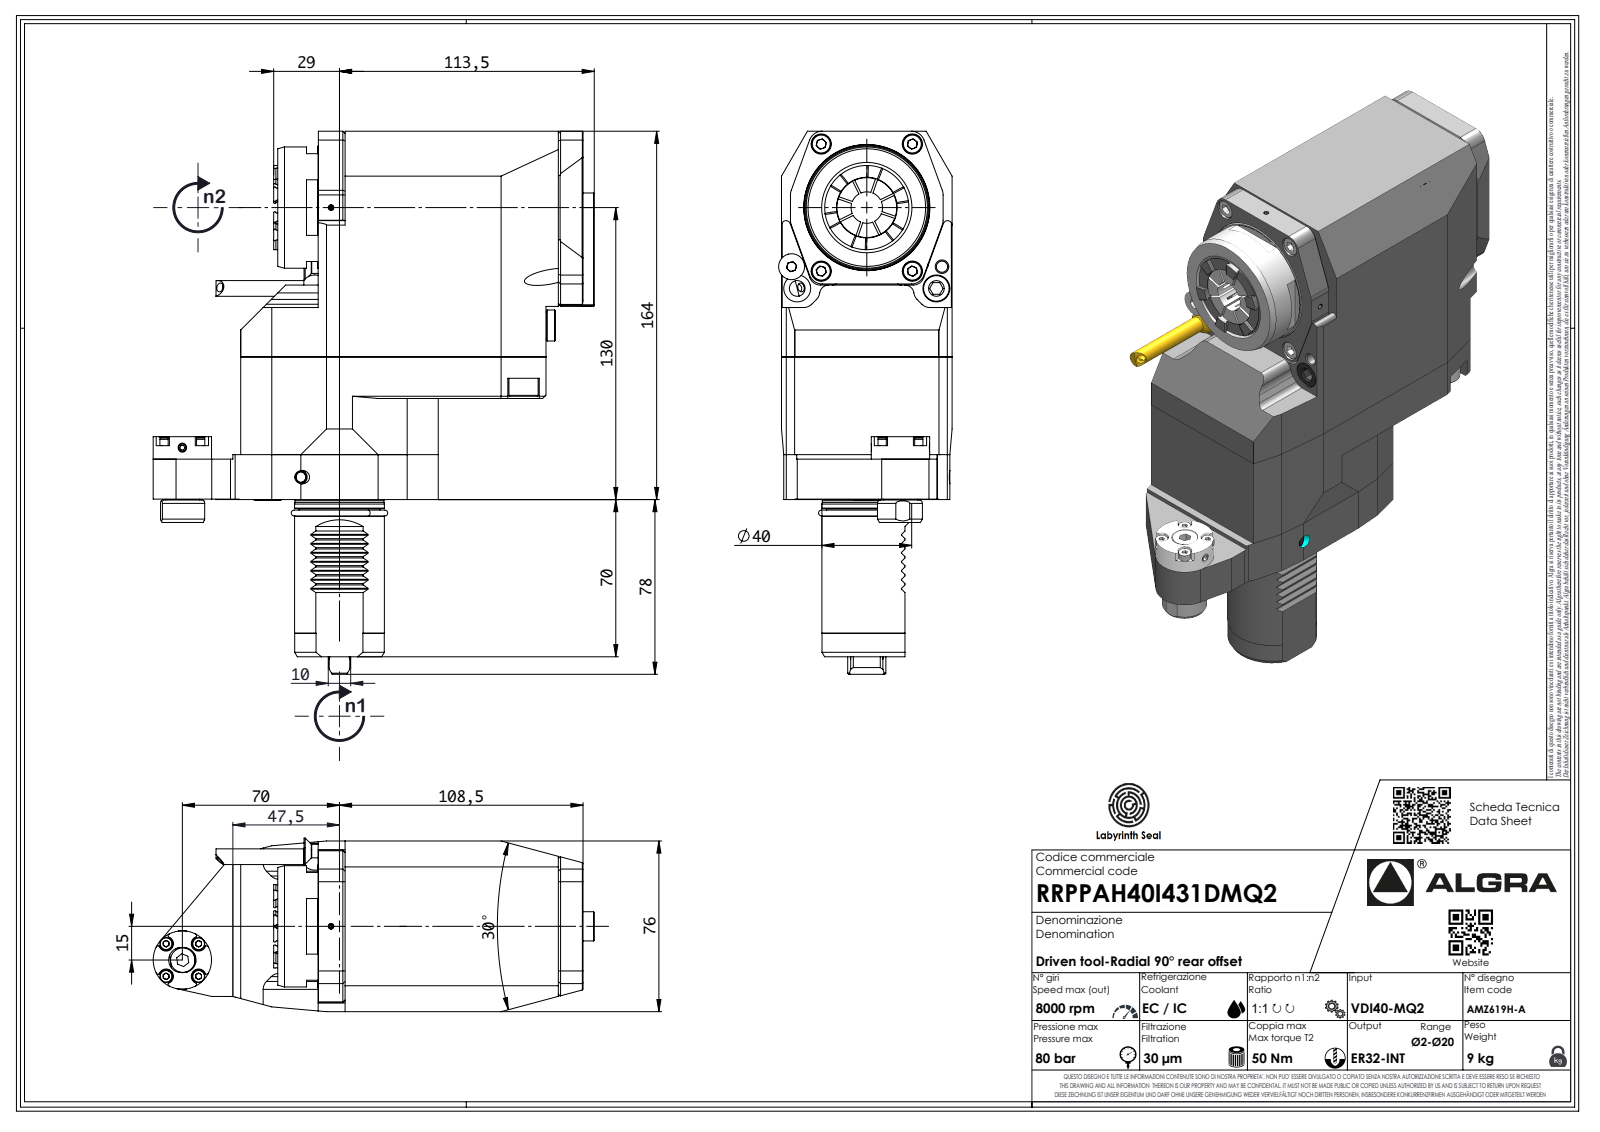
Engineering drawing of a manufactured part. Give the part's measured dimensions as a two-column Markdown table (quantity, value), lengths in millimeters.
| quantity | value |
| --- | --- |
| part name | RRPPAH40I431DMQ2 |
| STEP written by | SolidWorks 2023 (AUTOMOTIVE_DESIGN) |
| units | millimeters |
| bodies | 1 solid, 631 faces (418 planar, 99 cylindrical, 114 other) |
| overall size | 241.8 × 196.5 × 76 |
| volume | 1 507 000 mm³ |
| surface area | 101 957 mm² |
| round holes (diameter × count) | 2.1 × 1, 4 × 1 |
| round bosses / shafts (diameter × count) | 54 × 1, 40 × 1, 39.9 × 1, 39.6 × 1, 36 × 1, 26 × 1, 20 × 1, 15 × 1 |
| partial cylindrical surfaces (radius × count) | 6 × 10, 1 × 8, 3 × 8, 0.3 × 7, 0.33 × 7, 0.52 × 7, 3.7 × 7, 5 × 6 |
| main face-to-face distances | 76, 164, 136, 16.5, 88, 45, 119, 152.5, 48, 64.5 |
